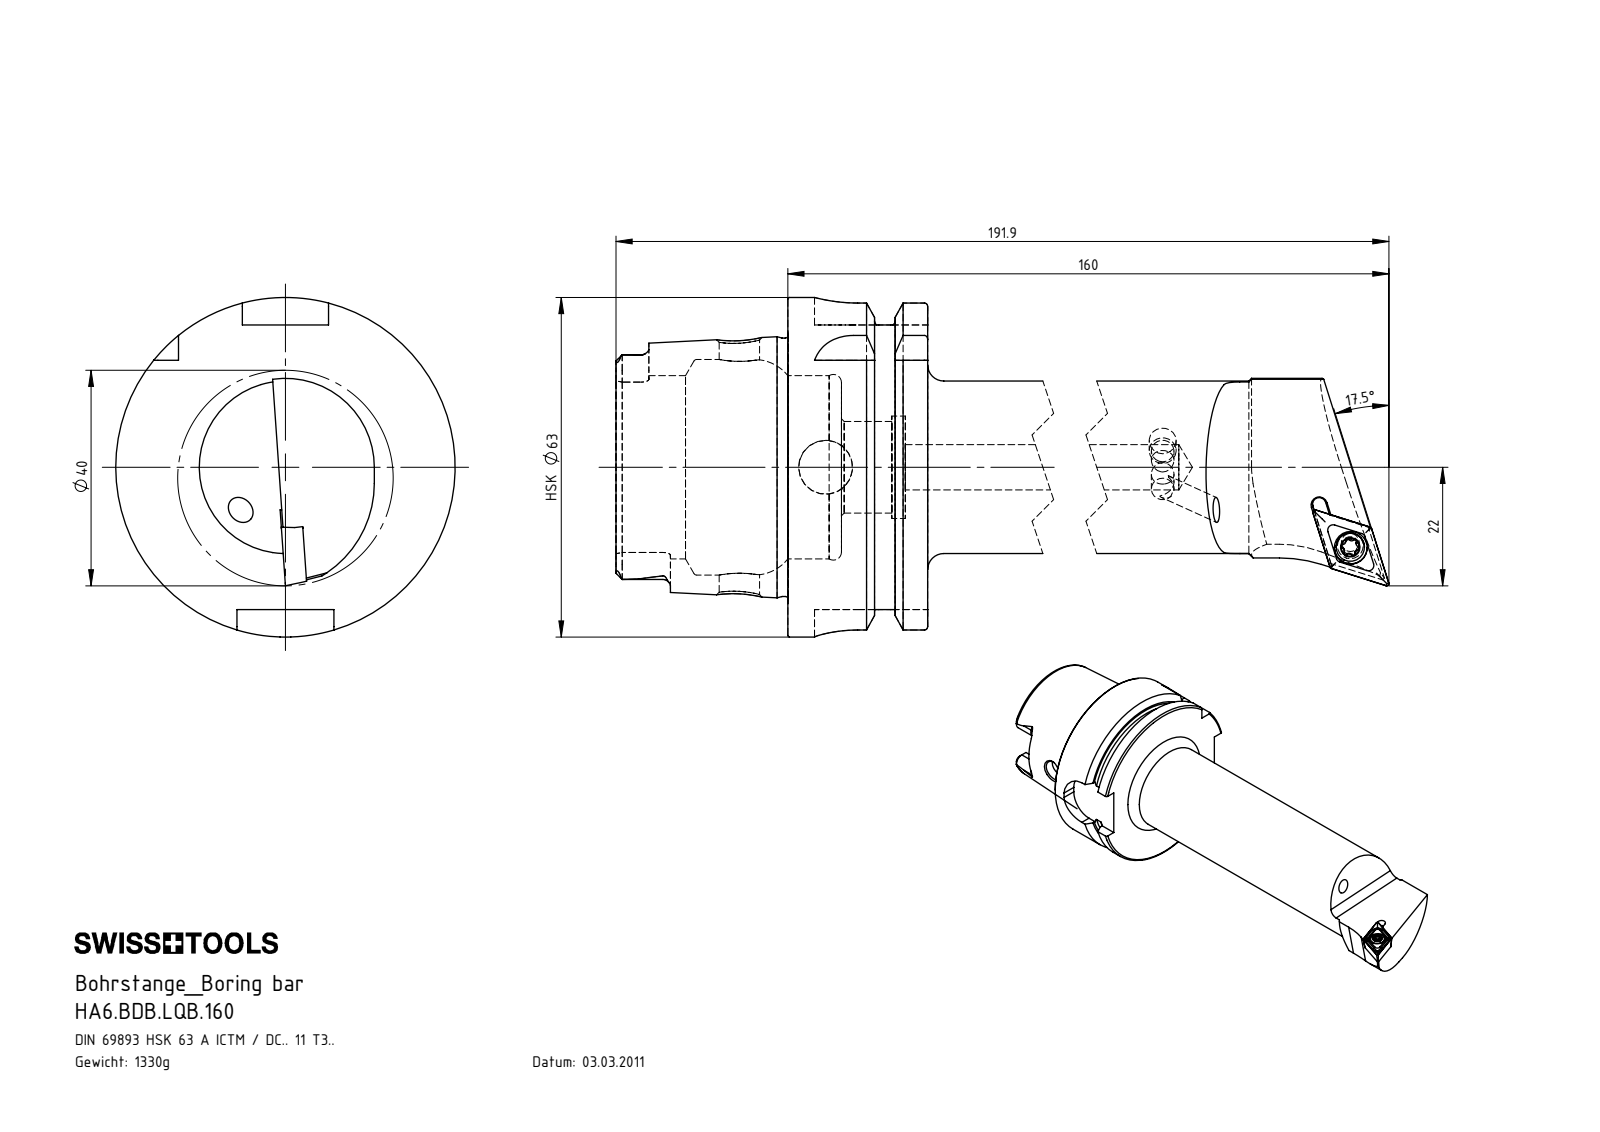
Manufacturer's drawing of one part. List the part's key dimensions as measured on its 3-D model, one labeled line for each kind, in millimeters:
Part name (STEP PRODUCT): WCB-ER2.001.009_A; HA6.BDB.LQB.160; DCMT11T304; HA6-BDB.LQB.160_B (+1 more)
STEP written by: SolidWorks 2017 (AUTOMOTIVE_DESIGN)
Units: millimetres
Bodies: 5 solids, 310 faces (79 planar, 92 cylindrical, 139 other)
Overall size (bounding box): 191.9 × 63 × 63
Volume: 169 143 mm³ · Surface area: 38 681 mm²
Round holes (diameter × count): ⌀4.2 ×2, ⌀3.3 ×1, ⌀4 ×1, ⌀4.4 ×1, ⌀6.1 ×1, ⌀7.5 ×1, ⌀8.4 ×1, ⌀10 ×1, ⌀17 ×1, ⌀19 ×1, ⌀34 ×1, ⌀40 ×1
Round bosses / shafts (diameter × count): ⌀63 ×1, ⌀54.95 ×1, ⌀47.94 ×1, ⌀32 ×1, ⌀5.25 ×1, ⌀5 ×1, ⌀4 ×1
Partial cylindrical surfaces — rounded edges, fillets, slot ends (radius × count): R0.34 ×6, R0.59 ×6, R1.4 ×6, R8 ×4, R2.82 ×2, R2.88 ×2, R1.25 ×1, R3 ×1
Main face-to-face distances: 25.95, 16, 9.95, 31.9, 41.85, 57.85, 52.8, 21.8, 11.85, 53.7
